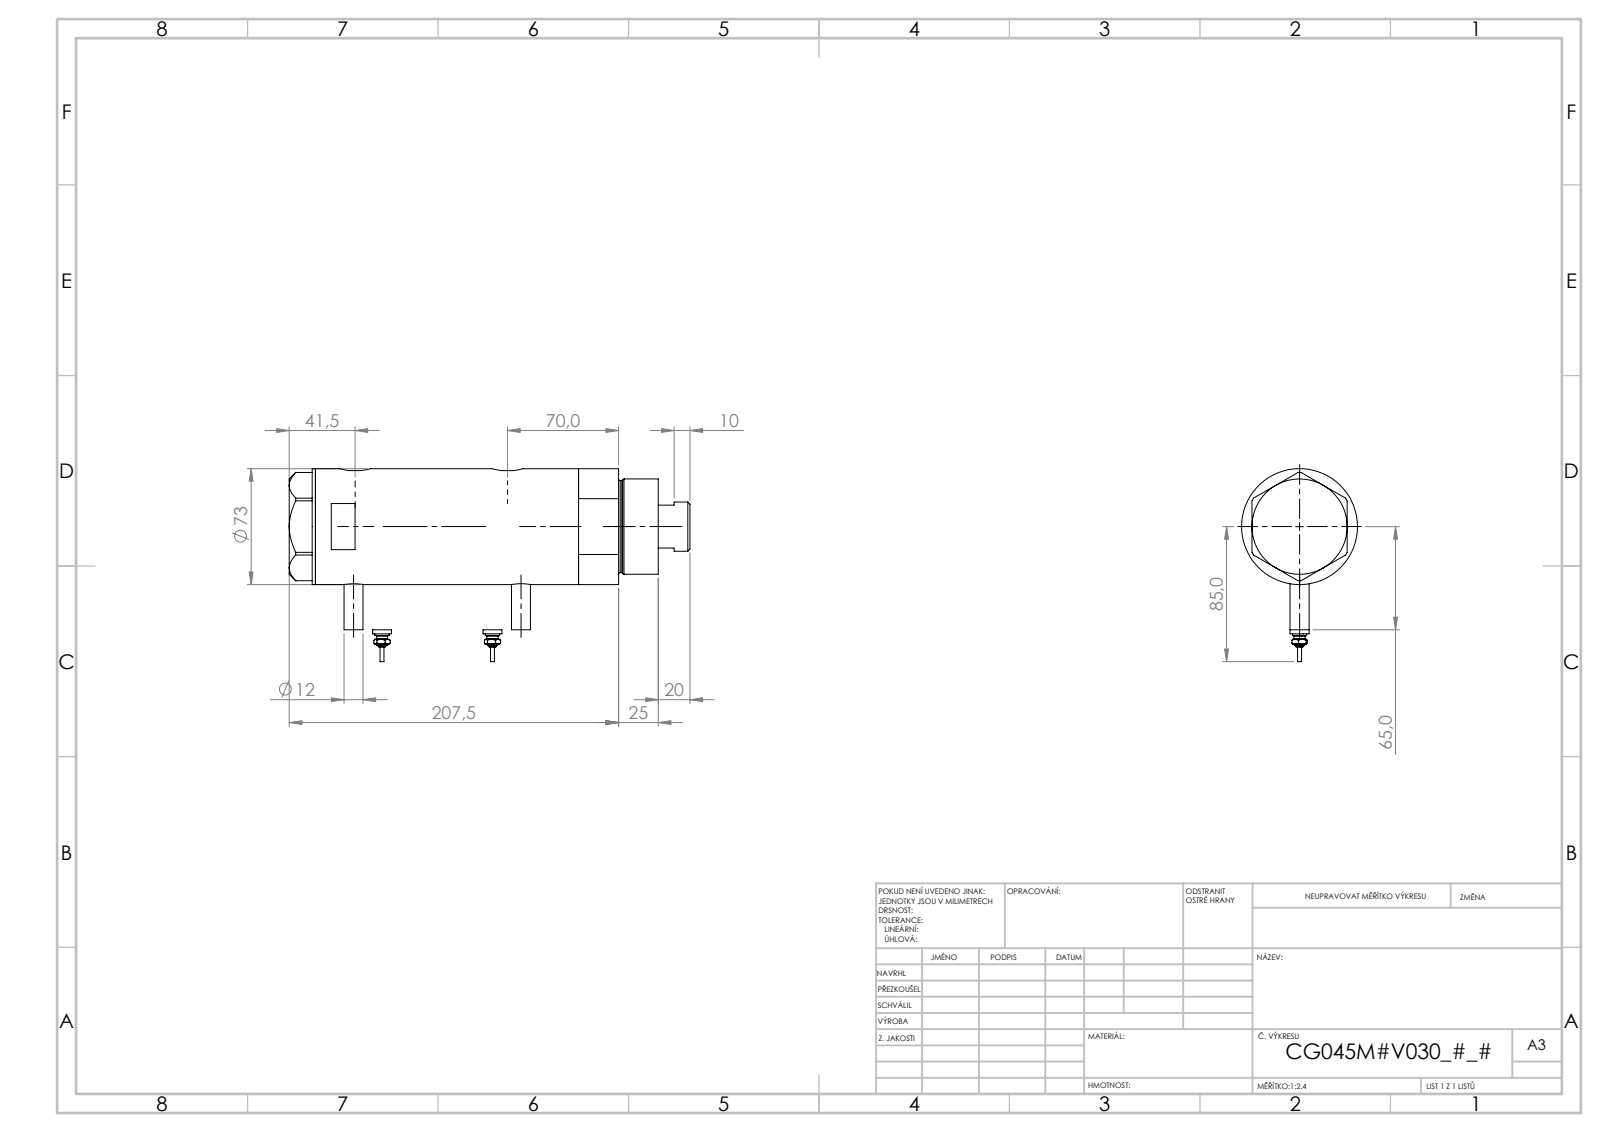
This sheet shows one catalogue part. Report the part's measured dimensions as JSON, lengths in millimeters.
{"part_name": "Switch; V270CG_BACK; V270CG_MIDDLE; V270CG_VC (+1 more)", "step_written_by": "SolidWorks 2019 (CONFIG_CONTROL_DESIGN)", "units": "millimeters", "bodies": {"solids": 6, "faces": 212, "planar": 77, "cylindrical": 71, "other": 64}, "overall_size": [252.5, 121.5, 73], "volume_mm3": 907883, "surface_area_mm2": 152546, "round_holes": [[12.5, 2], [13.16, 2], [10.5, 1], [32, 1], [33.5, 1], [45, 1], [48, 1], [64, 1]], "round_bosses_or_shafts": [[12, 4], [9, 2], [7, 2], [4.5, 2], [2.5, 2], [73, 1], [60, 1], [58, 1]], "partial_cylinders_radius": [[10, 2]], "face_to_face_distances": [95, 121, 26, 16.5, 42.5, 137.5, 2, 216, 232.5, 190], "hole_center_spacings": [1, 8.5, 96, 97, 104.5, 105.5]}
